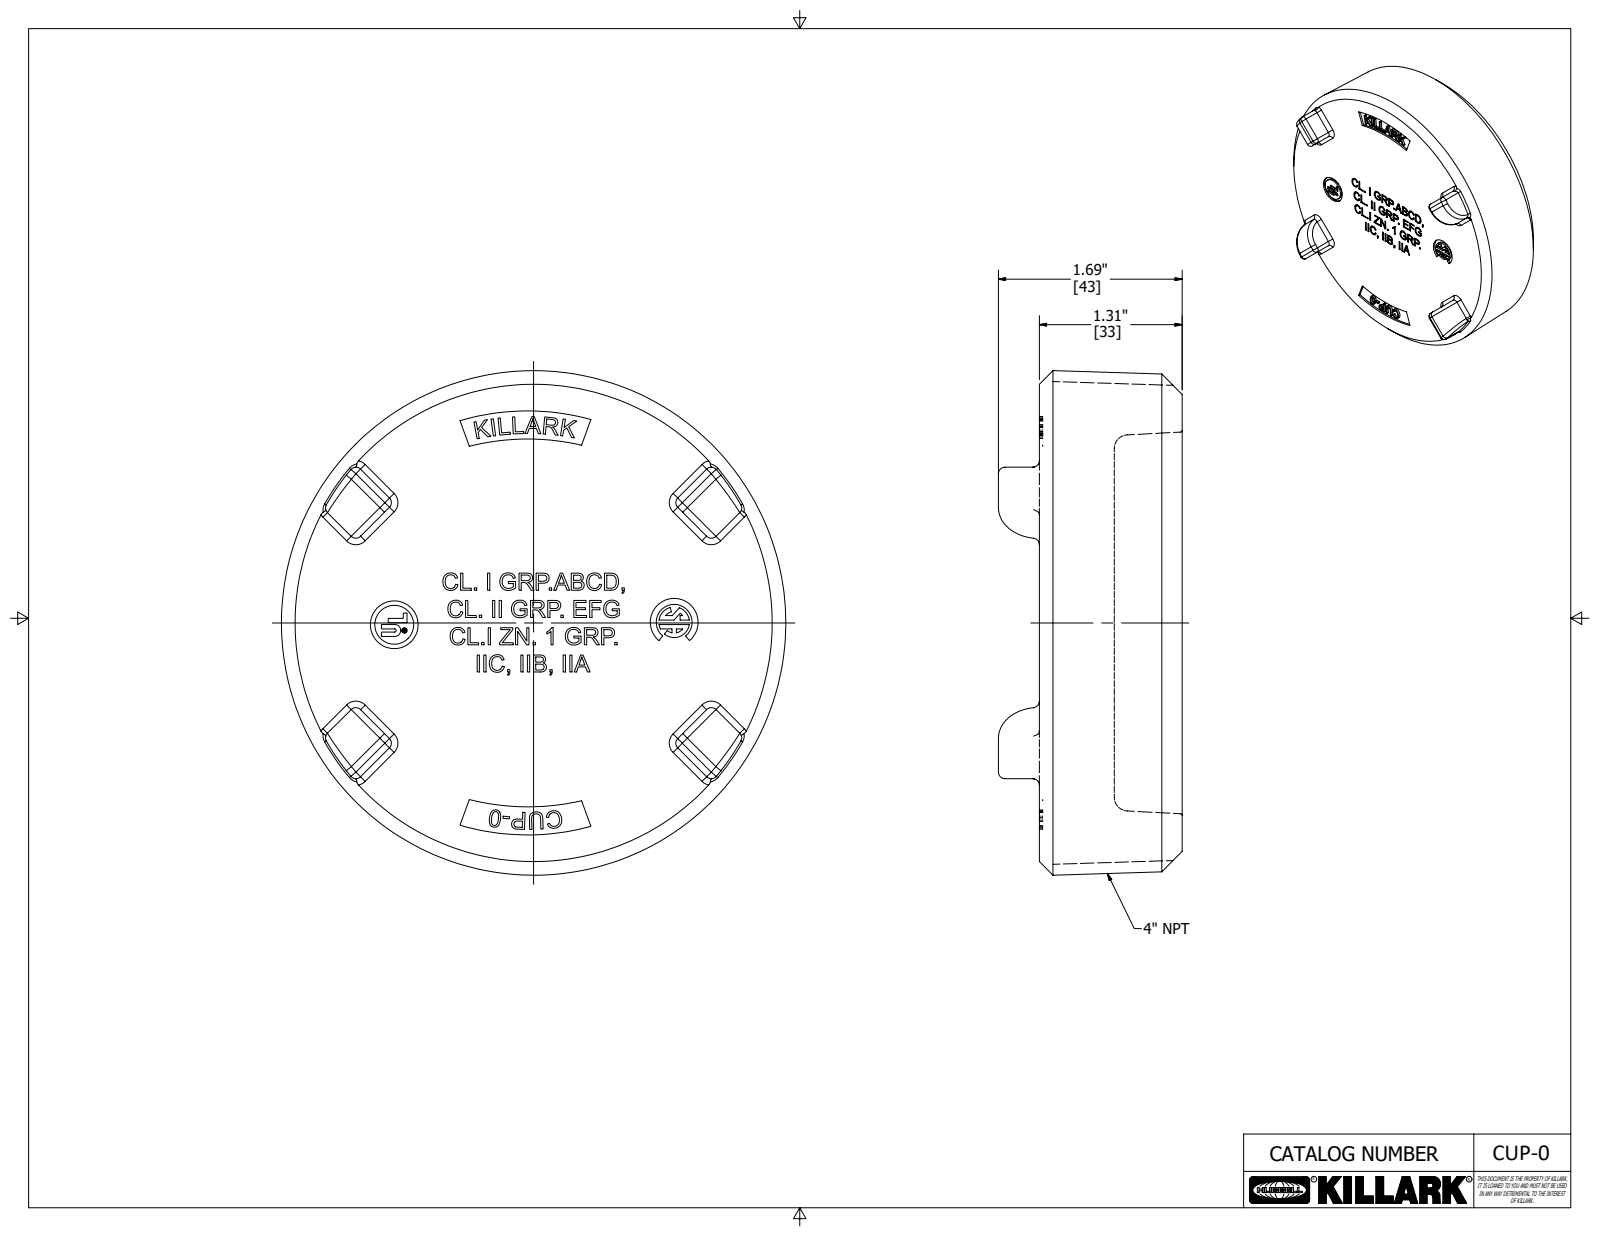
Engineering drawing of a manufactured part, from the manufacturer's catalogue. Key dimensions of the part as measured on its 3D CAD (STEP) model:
Part name (STEP PRODUCT): CUP-0_ETO
STEP written by: Autodesk Inventor 2020 (AUTOMOTIVE_DESIGN)
Units: inches
Bodies: 1 solid, 753 faces (494 planar, 56 cylindrical, 203 other)
Overall size (bounding box): 4.625 × 4.625 × 1.685
Volume: 15.75 in³ · Surface area: 59.08 in²
Round holes (diameter × count): ⌀0.049 ×1, ⌀0.437 ×1
Round bosses / shafts (diameter × count): ⌀0.356 ×1, ⌀0.043 ×1
Partial cylindrical surfaces — rounded edges, fillets, slot ends (radius × count): R0.06 ×28, R2.187 ×5, R0.375 ×4, R0.014 ×1, R0.055 ×1, R0.099 ×1, R0.14 ×1, R0.164 ×1
Main face-to-face distances: 0.687, 0.622, 1.31, 0.656, 0.031, 1.279, 1.559, 1.809, 0.25, 0.654
Hole centre spacings: 0.107
